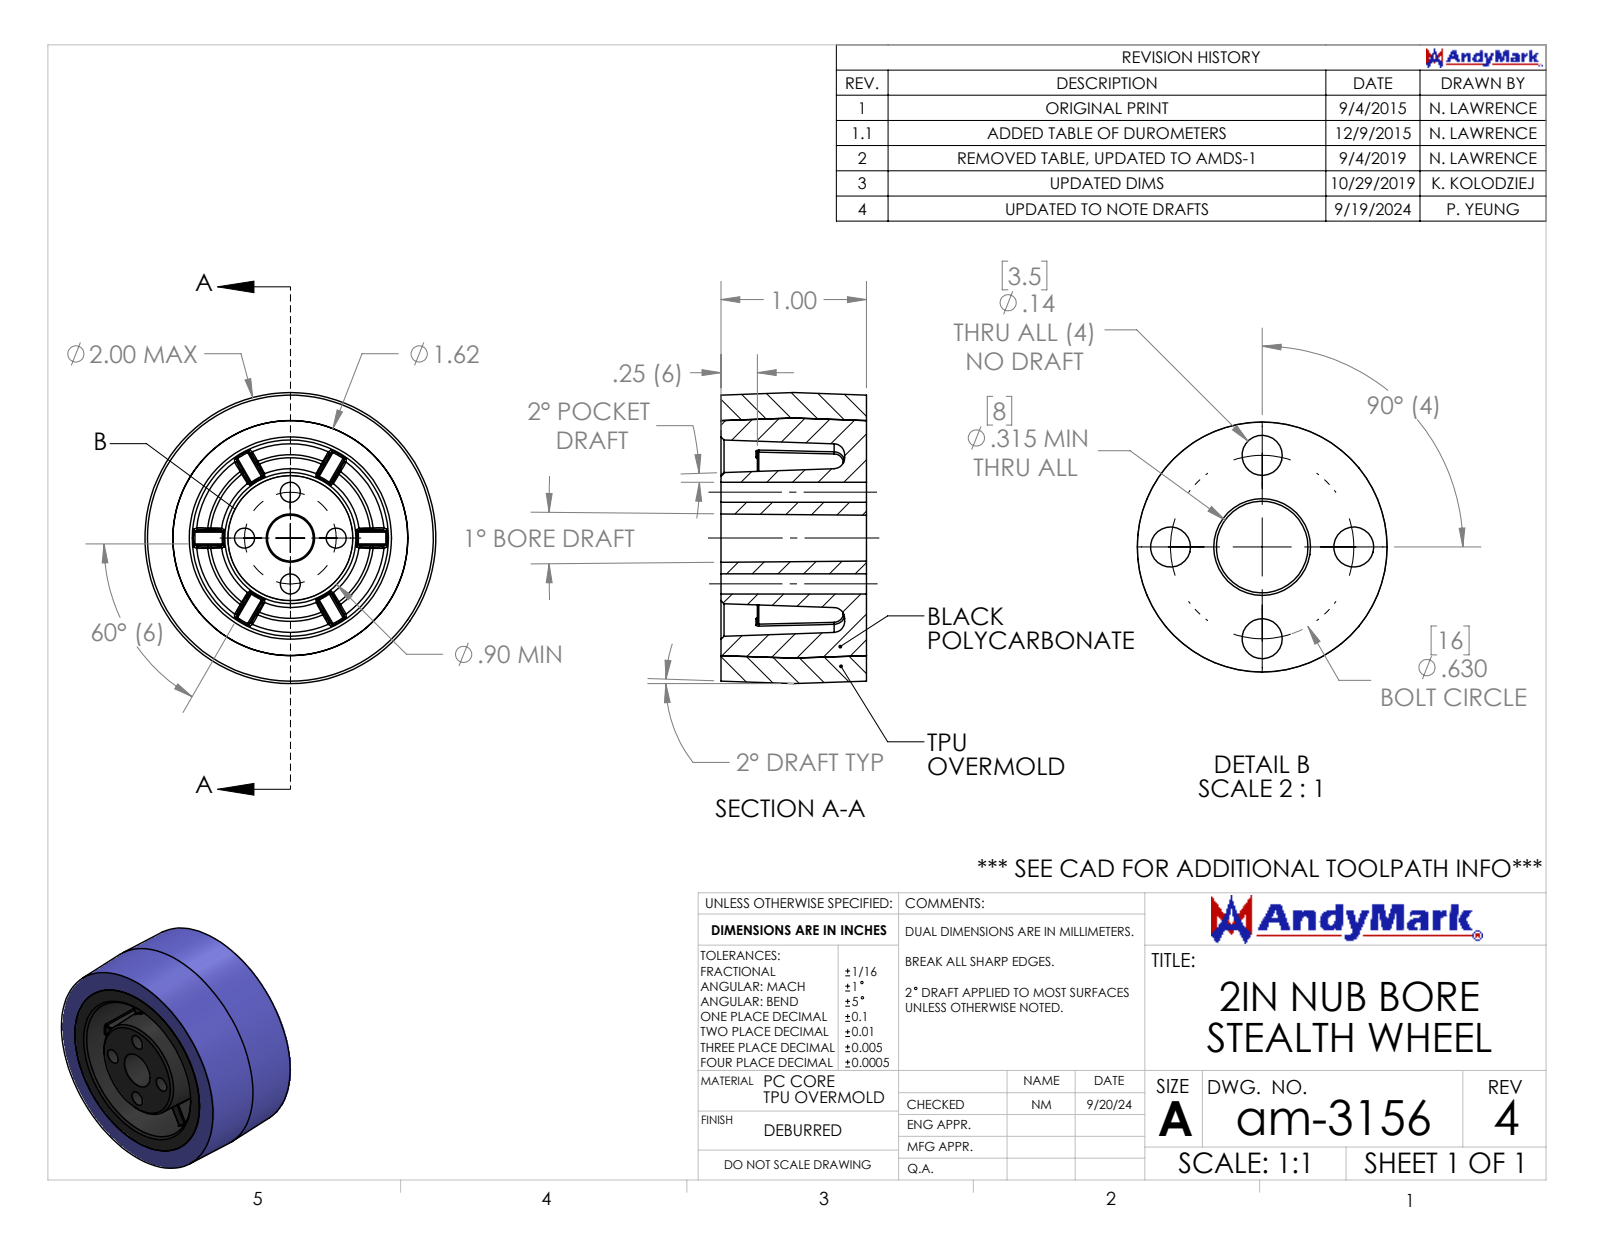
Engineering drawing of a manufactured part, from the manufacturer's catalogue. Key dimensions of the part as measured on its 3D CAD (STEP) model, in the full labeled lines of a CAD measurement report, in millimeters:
Part name (STEP PRODUCT): 2in Tread3; am-3156 2IN Stealth Wheel 8mm Nub Bore; 2in Wheel Intergrated 8mm Hub
STEP written by: SolidWorks 2024 (CONFIG_CONTROL_DESIGN)
Units: millimetres
Bodies: 2 solids, 181 faces (29 planar, 32 cylindrical, 120 other)
Overall size (bounding box): 50.8 × 50.8 × 25.4
Volume: 39 940 mm³ · Surface area: 20 020 mm²
Round holes (diameter × count): ⌀3.5 ×4
Partial cylindrical surfaces — rounded edges, fillets, slot ends (radius × count): R0.3 ×14
Main face-to-face distances: 25.4, 19.1, 6.4, 3.8, 15.2, 21.6
Hole centre spacings: 11.3, 16
